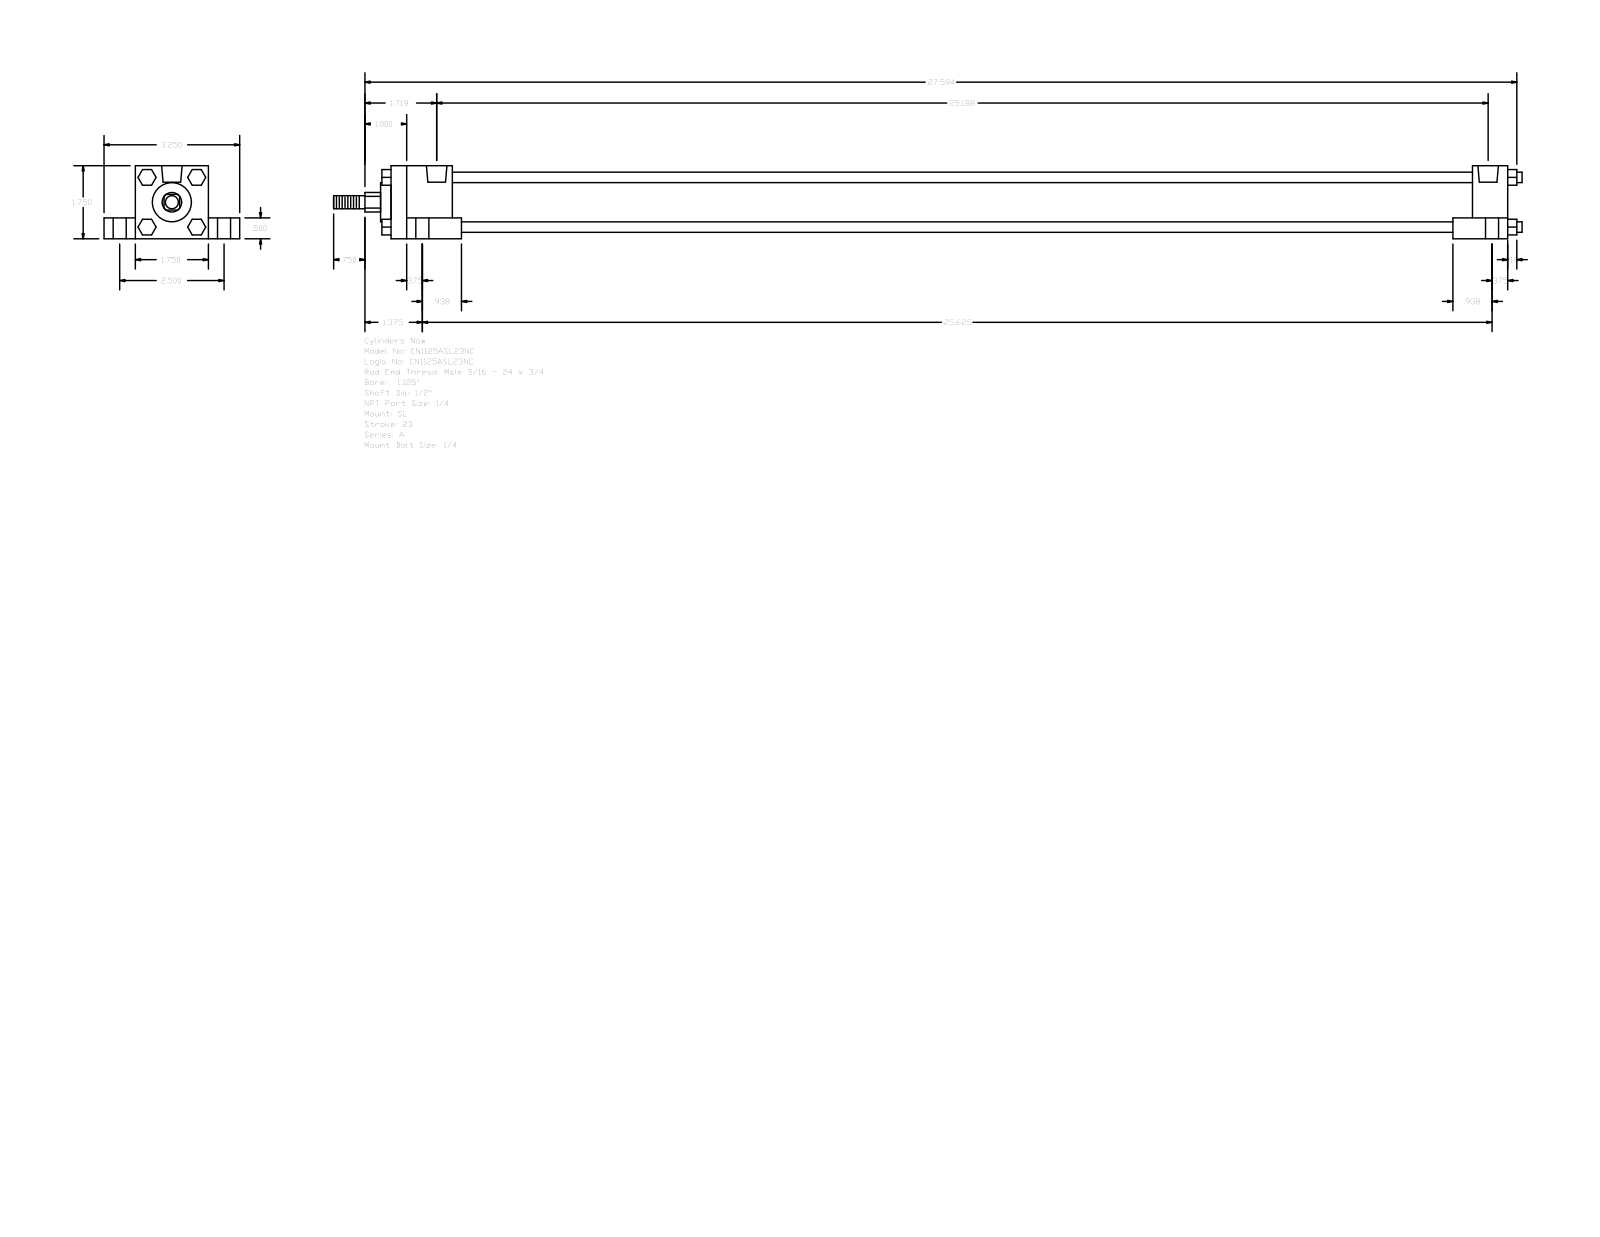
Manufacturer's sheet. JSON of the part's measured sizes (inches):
{"part_name": "A_SL__0112_0.5", "step_written_by": "GSSL Pune (CONFIG_CONTROL_DESIGN)", "units": "inches", "bodies": {"solids": 0, "faces": 150, "planar": 114, "cylindrical": 36, "other": 0}, "overall_size": [28.469, 3.25, 1.75], "round_holes": [[0.219, 4], [0.313, 4], [0.563, 4], [0.492, 2]], "round_bosses_or_shafts": [[0.25, 4], [1.255, 1], [0.937, 1], [0.5, 1], [0.313, 1]], "partial_cylinders_radius": [[0.234, 1]], "face_to_face_distances": [1.75, 1.25, 0.5, 0.75, 2.5, 26.75, 25.906, 0.844, 1.469, 24.437], "hole_center_spacings": [1.254, 1.26, 1.296, 1.315, 2.5, 25.063, 25.25, 25.312]}
